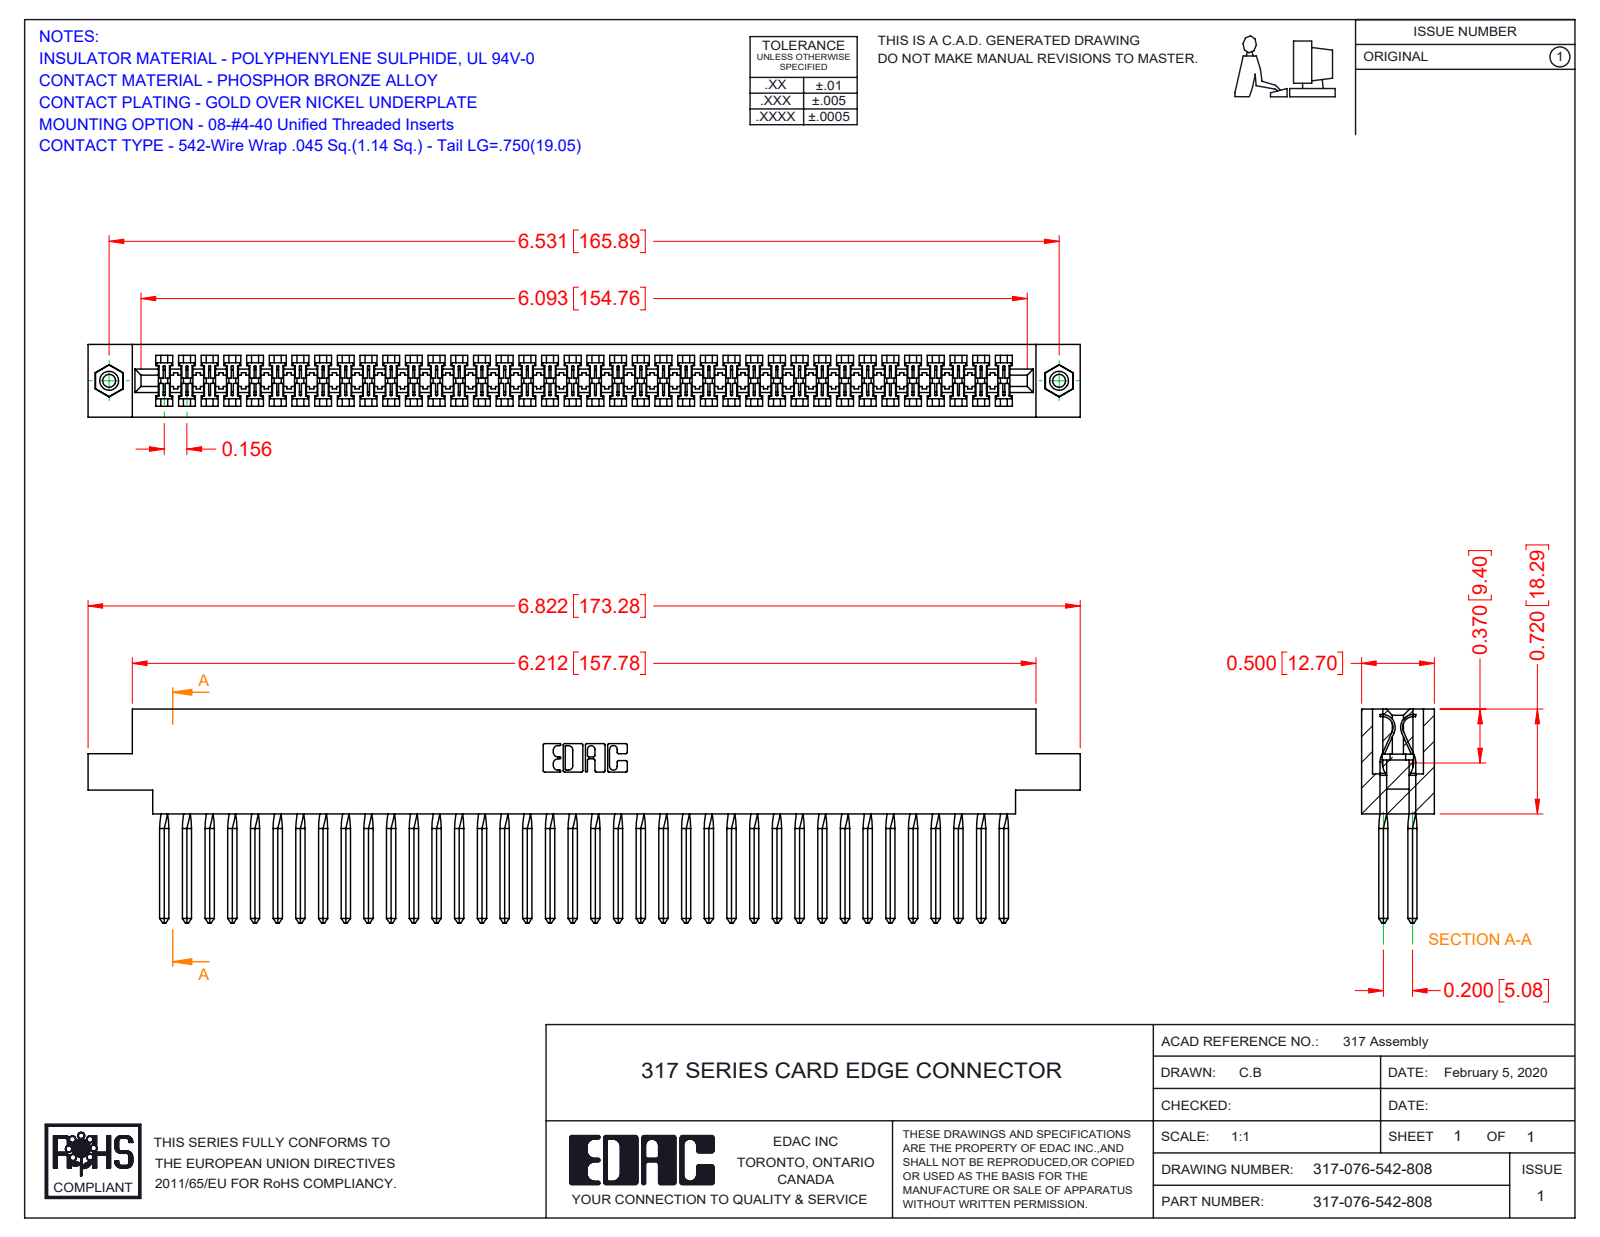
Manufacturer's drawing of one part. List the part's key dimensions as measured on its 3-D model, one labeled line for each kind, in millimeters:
Part name (STEP PRODUCT): 317-290-003_542; 345-250-001_345-250-003-102; 317-076-542-878; 317 Part_.156 Dia - TI
STEP written by: SolidWorks 2016 (CONFIG_CONTROL_DESIGN)
Units: millimetres
Bodies: 79 solids, 4494 faces (3586 planar, 588 cylindrical, 320 other)
Overall size (bounding box): 173.3 × 37.3 × 12.7
Volume: 28 230 mm³ · Surface area: 39 170 mm²
Round holes (diameter × count): ⌀2.3 ×2, ⌀3.2 ×2, ⌀4 ×2
Round bosses / shafts (diameter × count): ⌀3.9 ×2
Partial cylindrical surfaces — rounded edges, fillets, slot ends (radius × count): R0.2 ×152, R0.3 ×22, R0.2 ×6, R0.8 ×6, R0.7 ×3, R1.9 ×2, R2.3 ×2, R2.5 ×2
Main face-to-face distances: 12.7, 1.9, 10.8, 8.9, 5.1, 1.2, 3.3, 9.4, 1.3, 7.5
Hole centre spacings: 165.9
